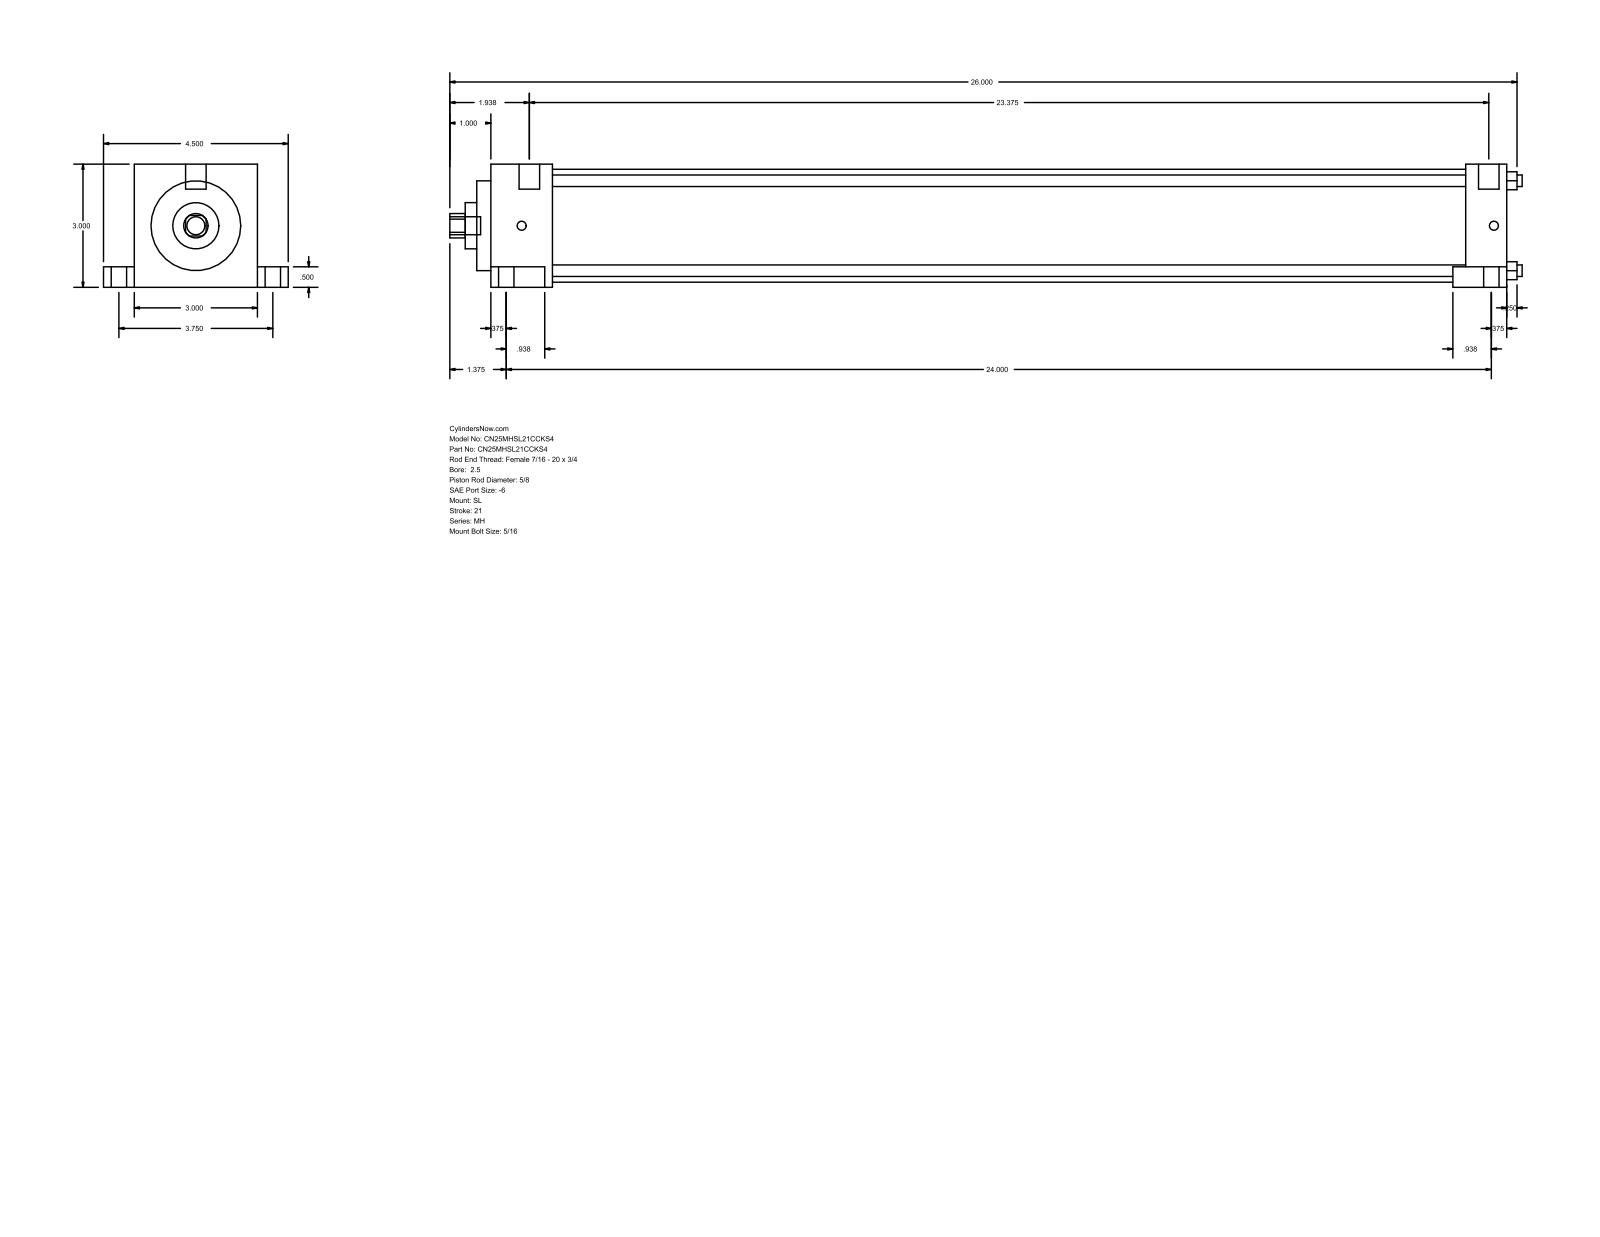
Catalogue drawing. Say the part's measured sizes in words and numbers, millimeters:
The part is named "MH_SL__0250_0.625". Its 3-D file was written by "GSSL Pune (CONFIG_CONTROL_DESIGN)". It is 0 solids with 86 faces: 61 planar, 25 cylindrical and 0 other. Overall it measures 663.58 by 114.3 by 76.2 millimeters. Round holes: 4 of diameter 7.14, 1 of diameter 15.88, 1 of diameter 28.57, 1 of diameter 55.55, 1 of diameter 69.85. Round bosses or shafts: 2 of diameter 15.88, 2 of diameter 9.53, 2 of diameter 5.56, 1 of diameter 12.7, 1 of diameter 11.11. Partial cylindrical surfaces (rounded edges, fillets, slot ends): 1 of radius 7.54. The main face-to-face distances are 76.2, 25.4, 611.98, 637.38, 12.7, 63.5, 19.05, 95.25, 31.75, 604.04. The hole center spacings are 39.33, 55.62, 78.66.
